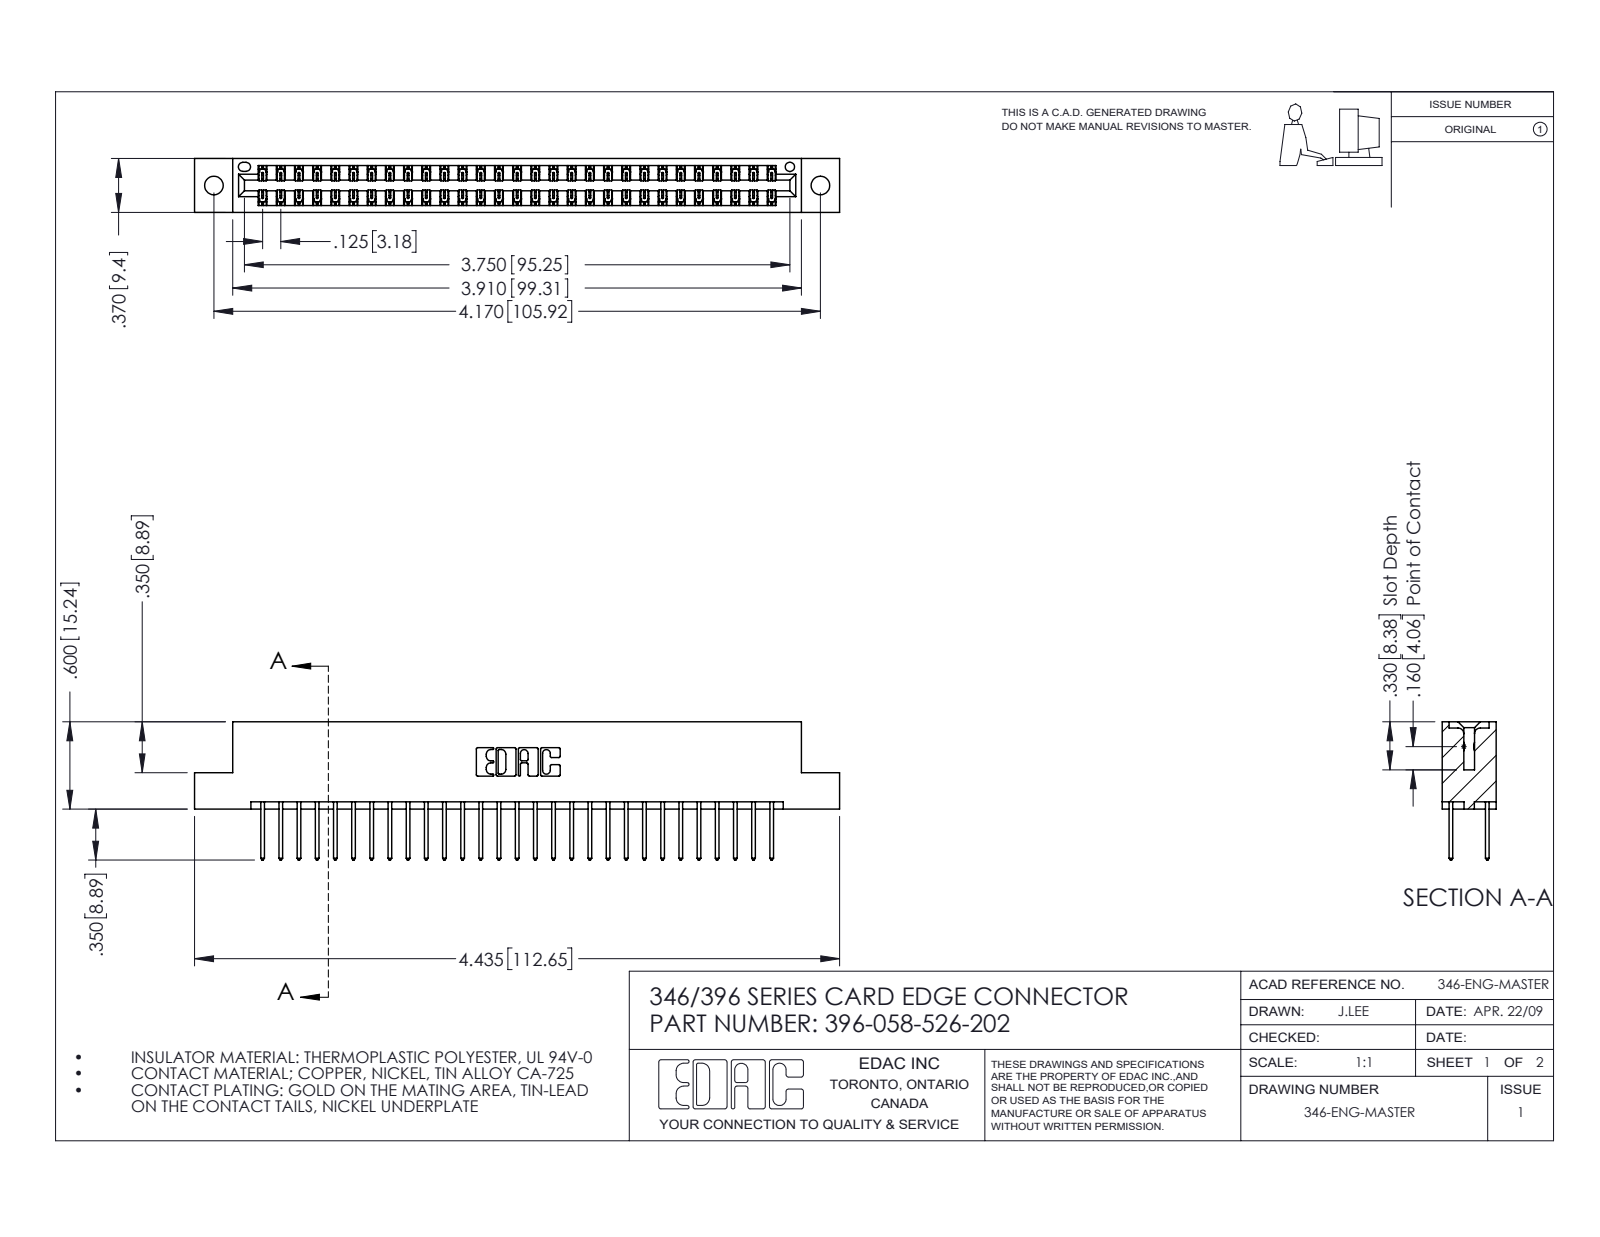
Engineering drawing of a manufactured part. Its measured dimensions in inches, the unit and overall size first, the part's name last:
Units: inches
Overall size (bounding box): 4.435 × 0.95 × 0.37
Round holes (diameter × count): ⌀0.128 ×2, ⌀0.064 ×1
Partial cylindrical surfaces — rounded edges, fillets, slot ends (radius × count): R0.006 ×87, R0.01 ×58, R0.01 ×22, R0.007 ×6, R0.031 ×6, R0.026 ×3, R0.014 ×2, R0.022 ×2
Main face-to-face distances: 0.048, 0.322, 0.25, 0.37, 0.072, 0.298, 0.025, 0.275, 0.148, 0.222
Hole centre spacings: 0.246, 3.962, 4.17
Volume: 0.668 in³ · Surface area: 23.24 in²
Bodies: 59 solids, 3138 faces (2106 planar, 1032 cylindrical, 0 other)
Part name (STEP PRODUCT): 345-292-001_345-293-126; 346 Part_Flush Mounting Lugs - 0.128 Dia; 396-058-526-202
STEP written by: SolidWorks 2016 (CONFIG_CONTROL_DESIGN)
